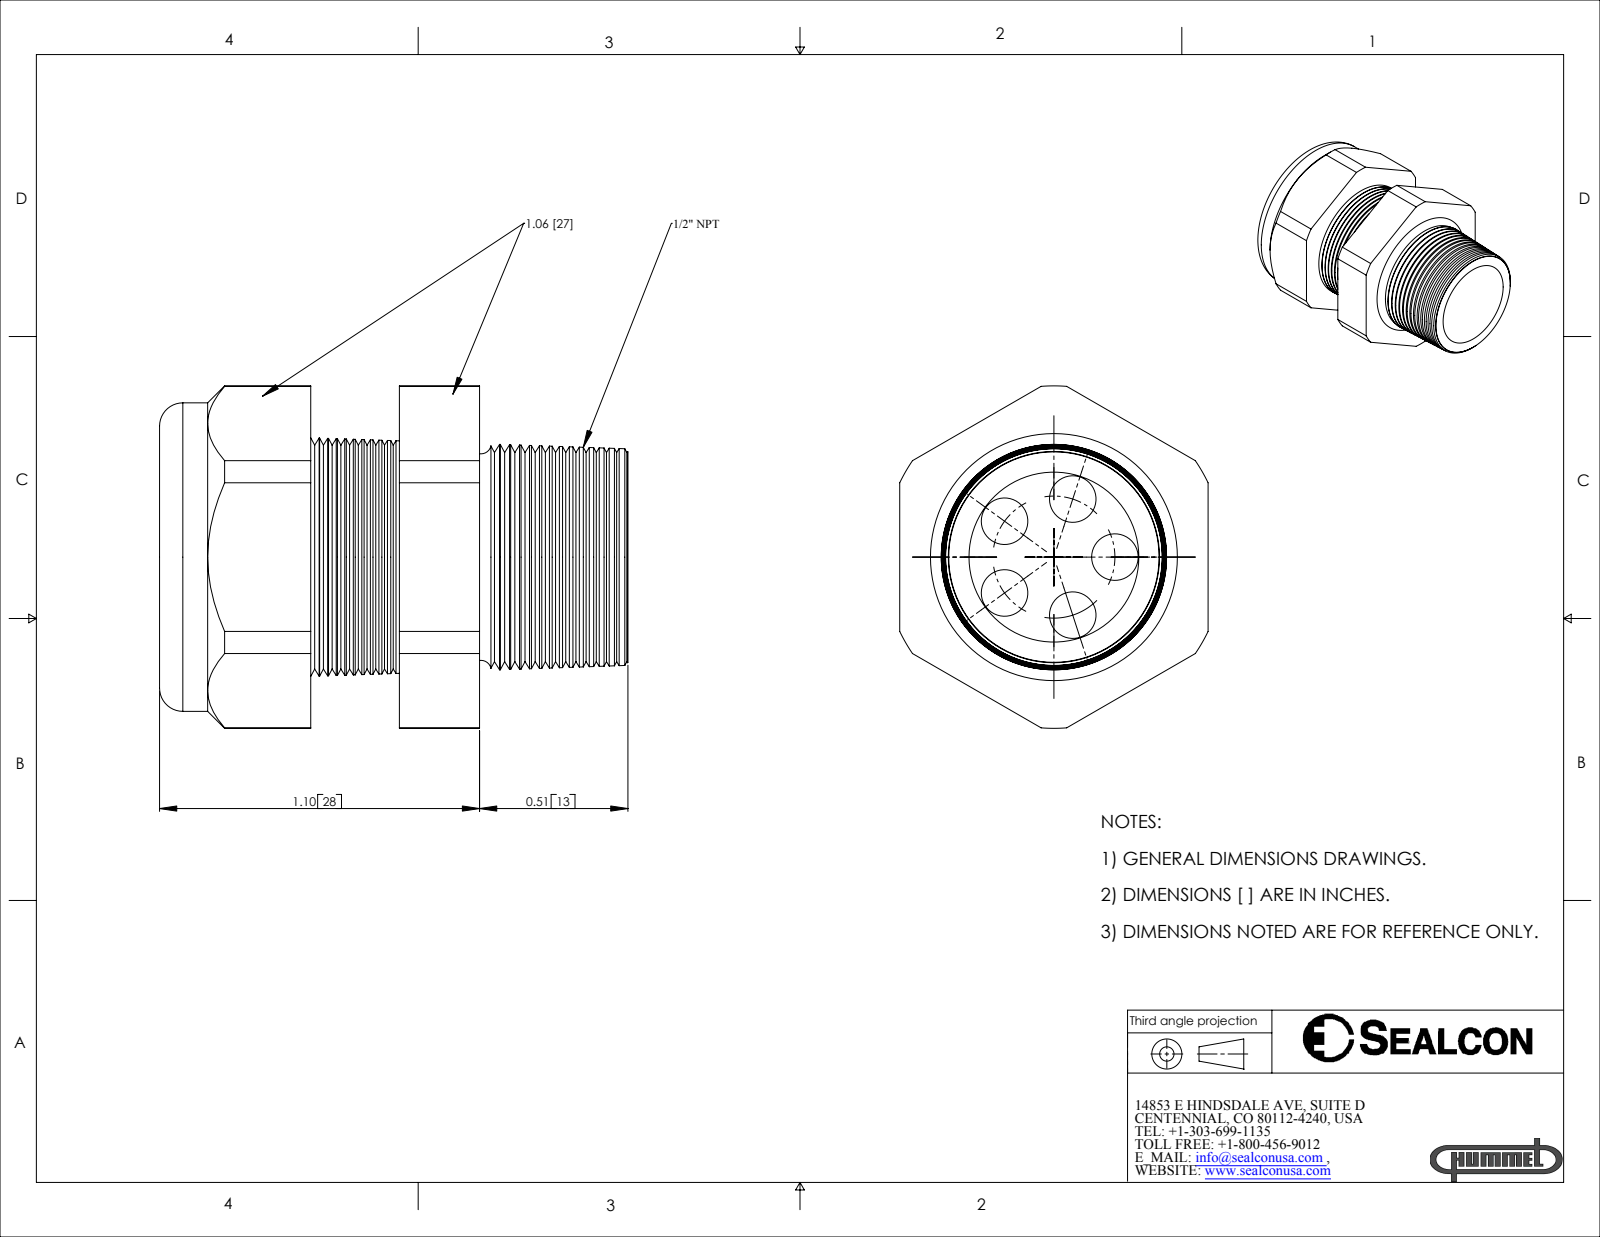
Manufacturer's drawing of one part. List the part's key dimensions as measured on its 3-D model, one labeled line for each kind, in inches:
Part name (STEP PRODUCT): CD16N4-GY
STEP written by: SolidWorks 2007 (CONFIG_CONTROL_DESIGN)
Units: inches
Bodies: 2 solids, 208 faces (20 planar, 30 cylindrical, 158 other)
Overall size (bounding box): 1.61 × 1.177 × 1.06
Volume: 0.73 in³ · Surface area: 13.24 in²
Round holes (diameter × count): ⌀0.16 ×5, ⌀0.58 ×1, ⌀0.6 ×1
Round bosses / shafts (diameter × count): ⌀1.06 ×1
Partial cylindrical surfaces — rounded edges, fillets, slot ends (radius × count): R0.588 ×1
Main face-to-face distances: 1.06, 0.305, 0.58, 0.276, 0.52, 0.824, 1.1, 0.35, 0.17, 0.474
Hole centre spacings: 0.21, 0.399, 0.246, 0.247
